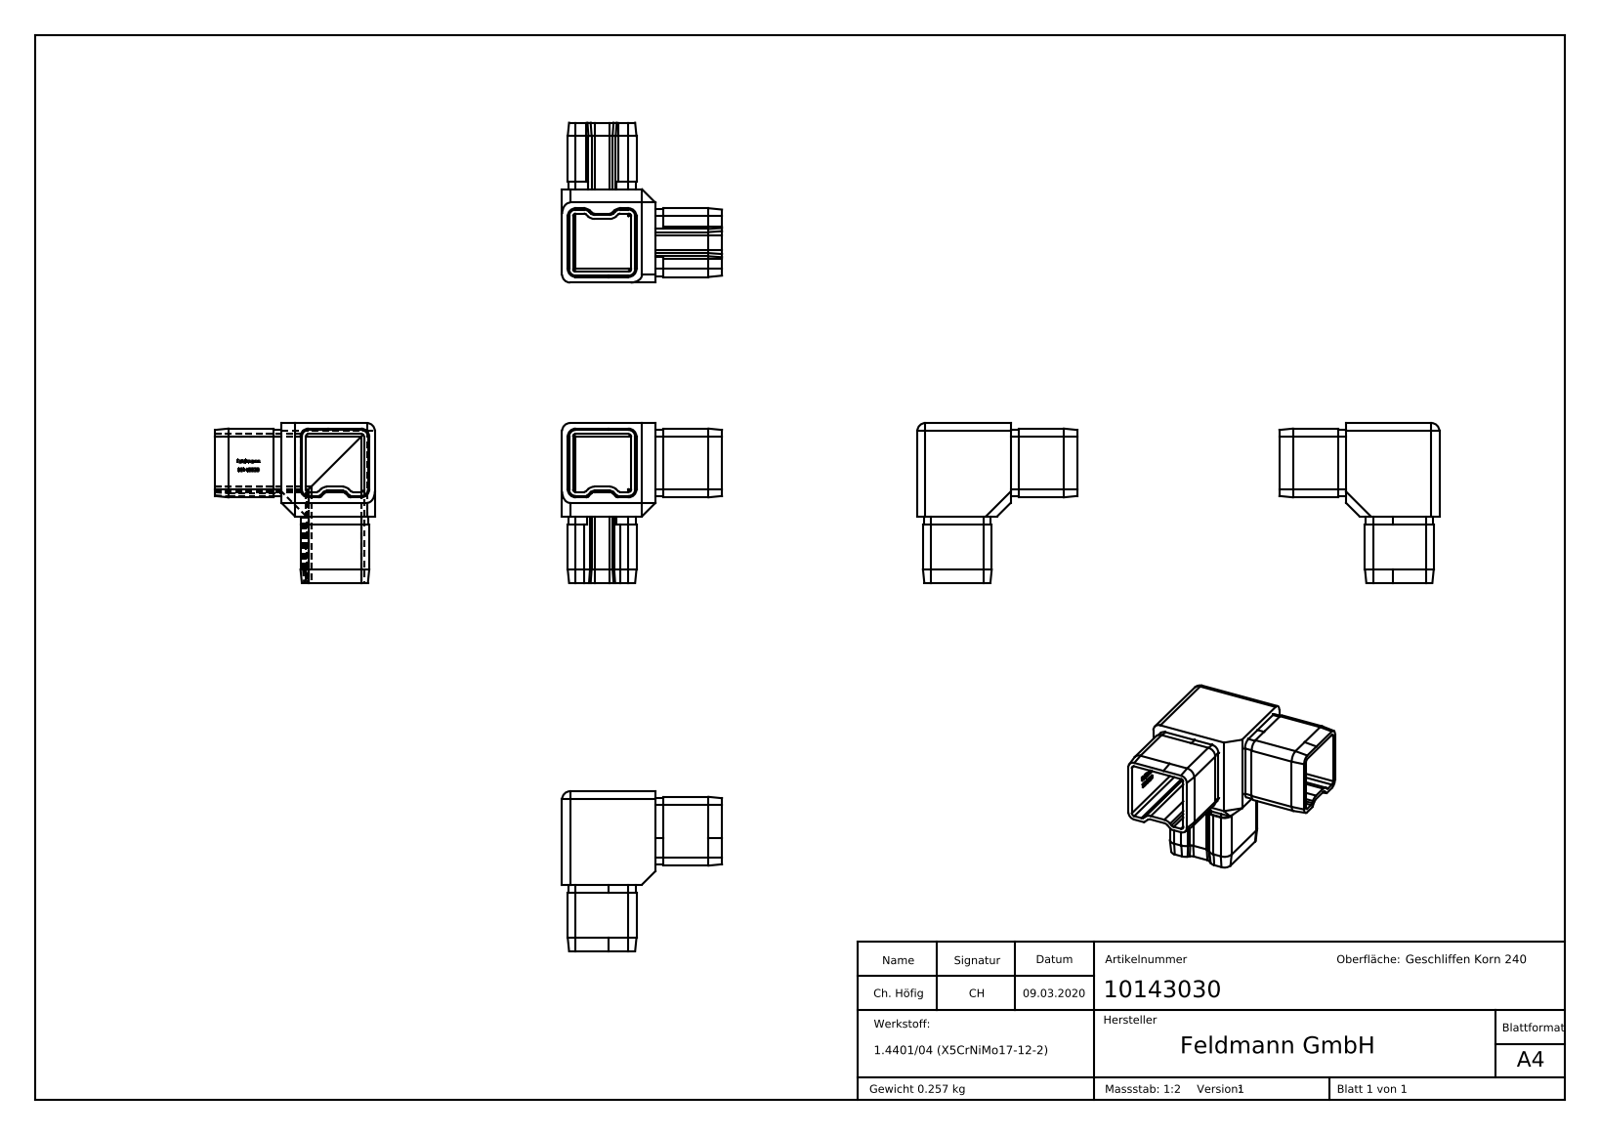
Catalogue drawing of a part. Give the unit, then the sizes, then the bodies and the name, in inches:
Units: inches
Overall size (bounding box): 2.362 × 2.362 × 2.362
Partial cylindrical surfaces — rounded edges, fillets, slot ends (radius × count): R0.118 ×17, R0.039 ×12, R0.106 ×12, R0.05 ×10, R0.059 ×6, R0.138 ×6, R0.129 ×2
Main face-to-face distances: 0.079, 0.858, 0.937, 0.161, 1.02, 0.083, 1.098, 1.016, 1.378, 1.295
Volume: 1.959 in³ · Surface area: 36.02 in²
Bodies: 1 solid, 436 faces (242 planar, 66 cylindrical, 128 other)
Part name (STEP PRODUCT): 10143030
STEP written by: SolidWorks 2015 (CONFIG_CONTROL_DESIGN)
